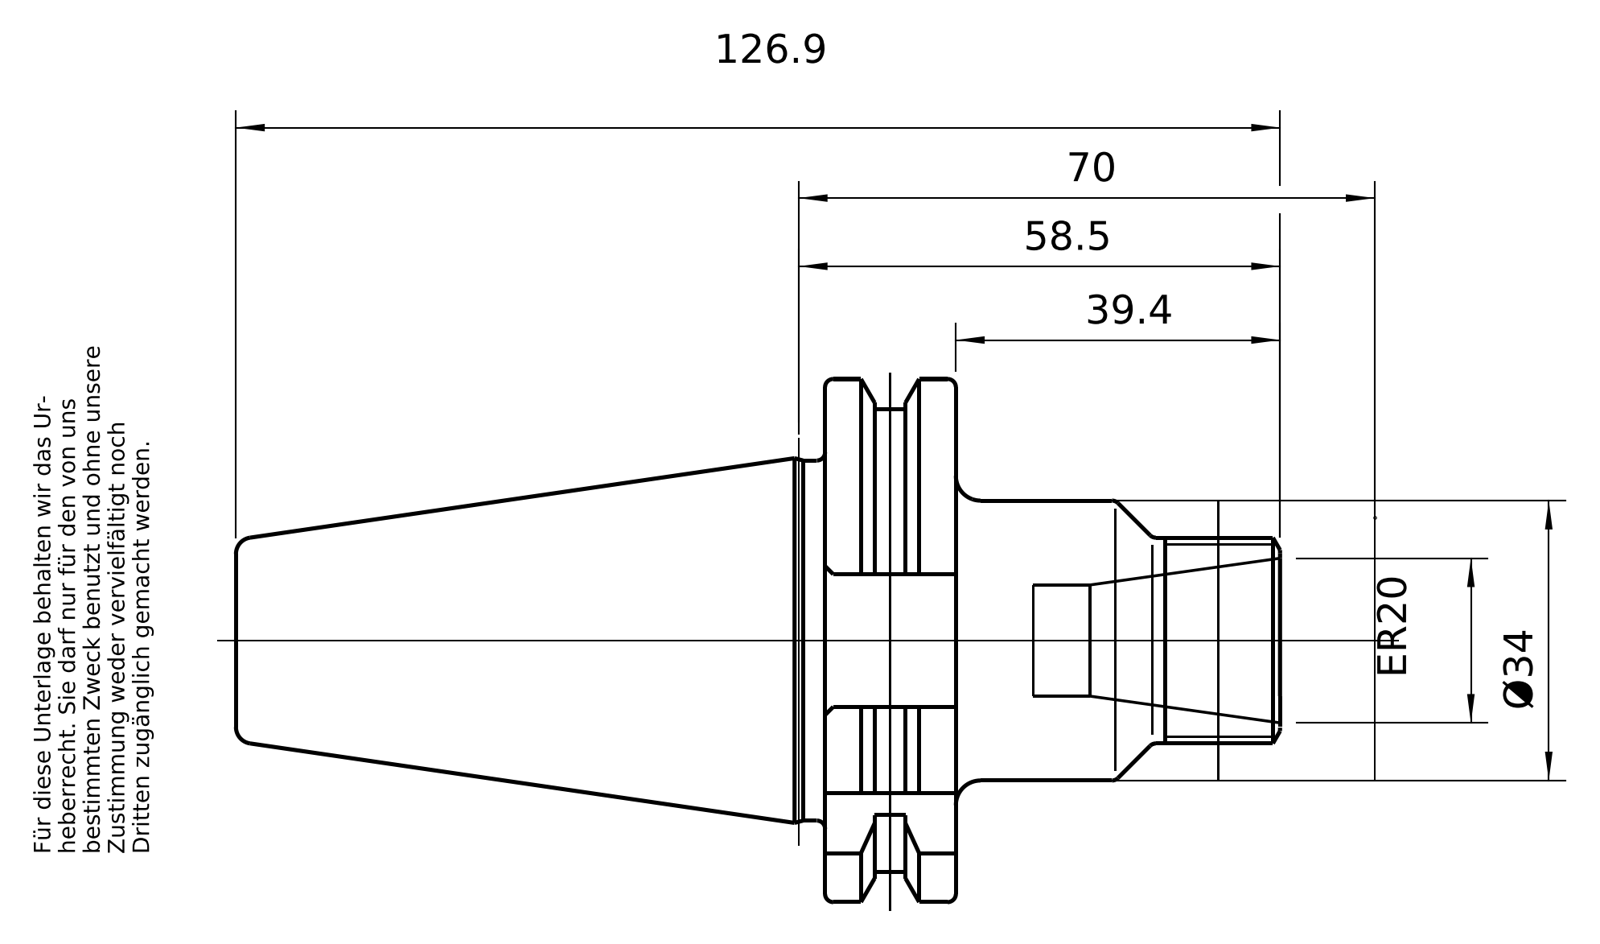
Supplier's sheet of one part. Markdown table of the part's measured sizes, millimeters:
| quantity | value |
| --- | --- |
| part name | 40-320-20; 83-912-20; 40-320-20_ASM |
| STEP written by | PRO/ENGINEER BY PARAMETRIC TECHNOLOGY CORPORATION, 2010430 (CONFIG_CONTROL_DESIGN) |
| units | millimeters |
| bodies | 2 solids, 125 faces (29 planar, 28 cylindrical, 68 other) |
| overall size | 138.25 × 63.52 × 61.42 |
| volume | 143 700 mm³ |
| surface area | 28 224 mm² |
| round holes (diameter × count) | 13.5 × 1, 13.84 × 1, 17.01 × 1, 17.5 × 1 |
| round bosses / shafts (diameter × count) | 43.75 × 1, 34 × 1, 25 × 1, 16.01 × 1 |
| partial cylindrical surfaces (radius × count) | 1.35 × 1, 28 × 1, 31.76 × 1 |
| main face-to-face distances | 15.85, 47.8, 31.95, 30, 66.8, 50.95, 19, 6.9, 23.1, 47.4 |
